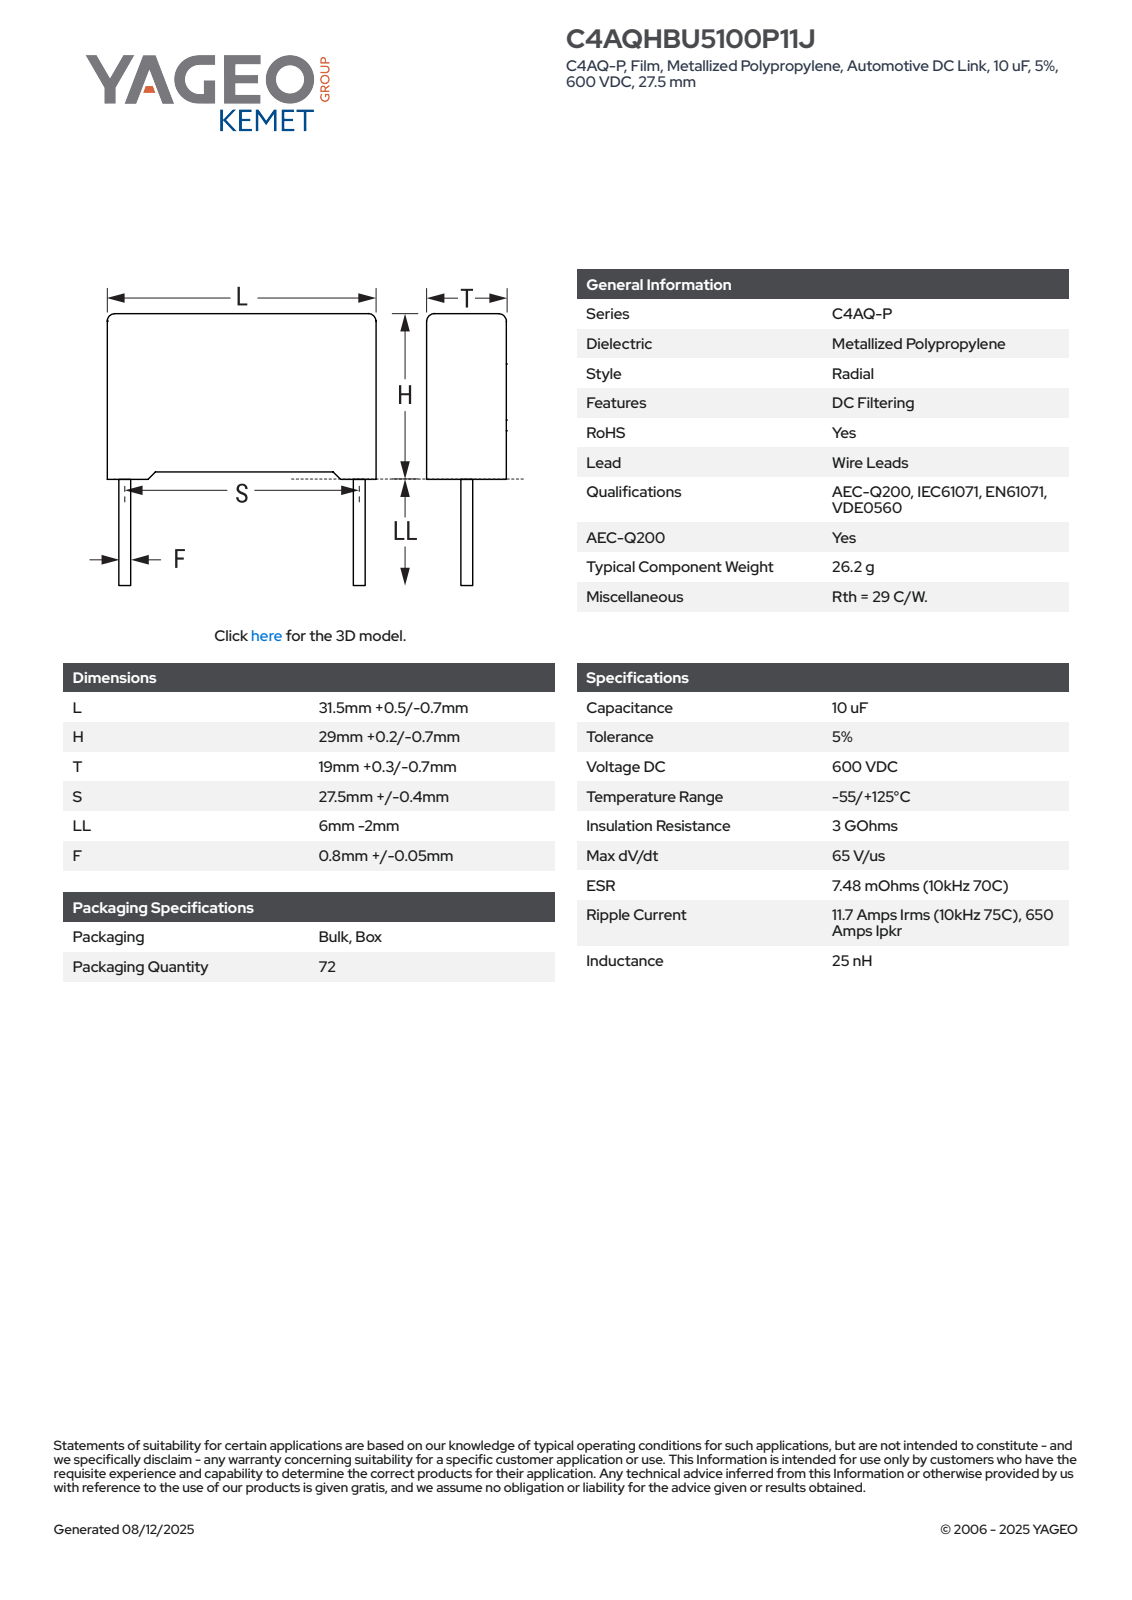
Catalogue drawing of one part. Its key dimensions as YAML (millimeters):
part_name: "CFR_RB2CFP_31.5X29X19_L32H29.2T19.3S27.5LL4F0.85"
step_written_by: "SolidWorks 2014 (AUTOMOTIVE_DESIGN)"
units: millimeters
bodies: {solids: 4, faces: 85, planar: 77, cylindrical: 8, other: 0}
overall_size: [33.2, 32, 19.3]
volume: 17498
surface_area: 4304
round_bosses_or_shafts:
  - {diameter: 0.85, count: 2}
partial_cylinders:
  - {radius: 0.5, count: 4}
face_to_face_distances: [19.3, 32, 28.19, 28.45, 0.75, 1.01, 29.2, 1.07, 30.93, 19.31]
